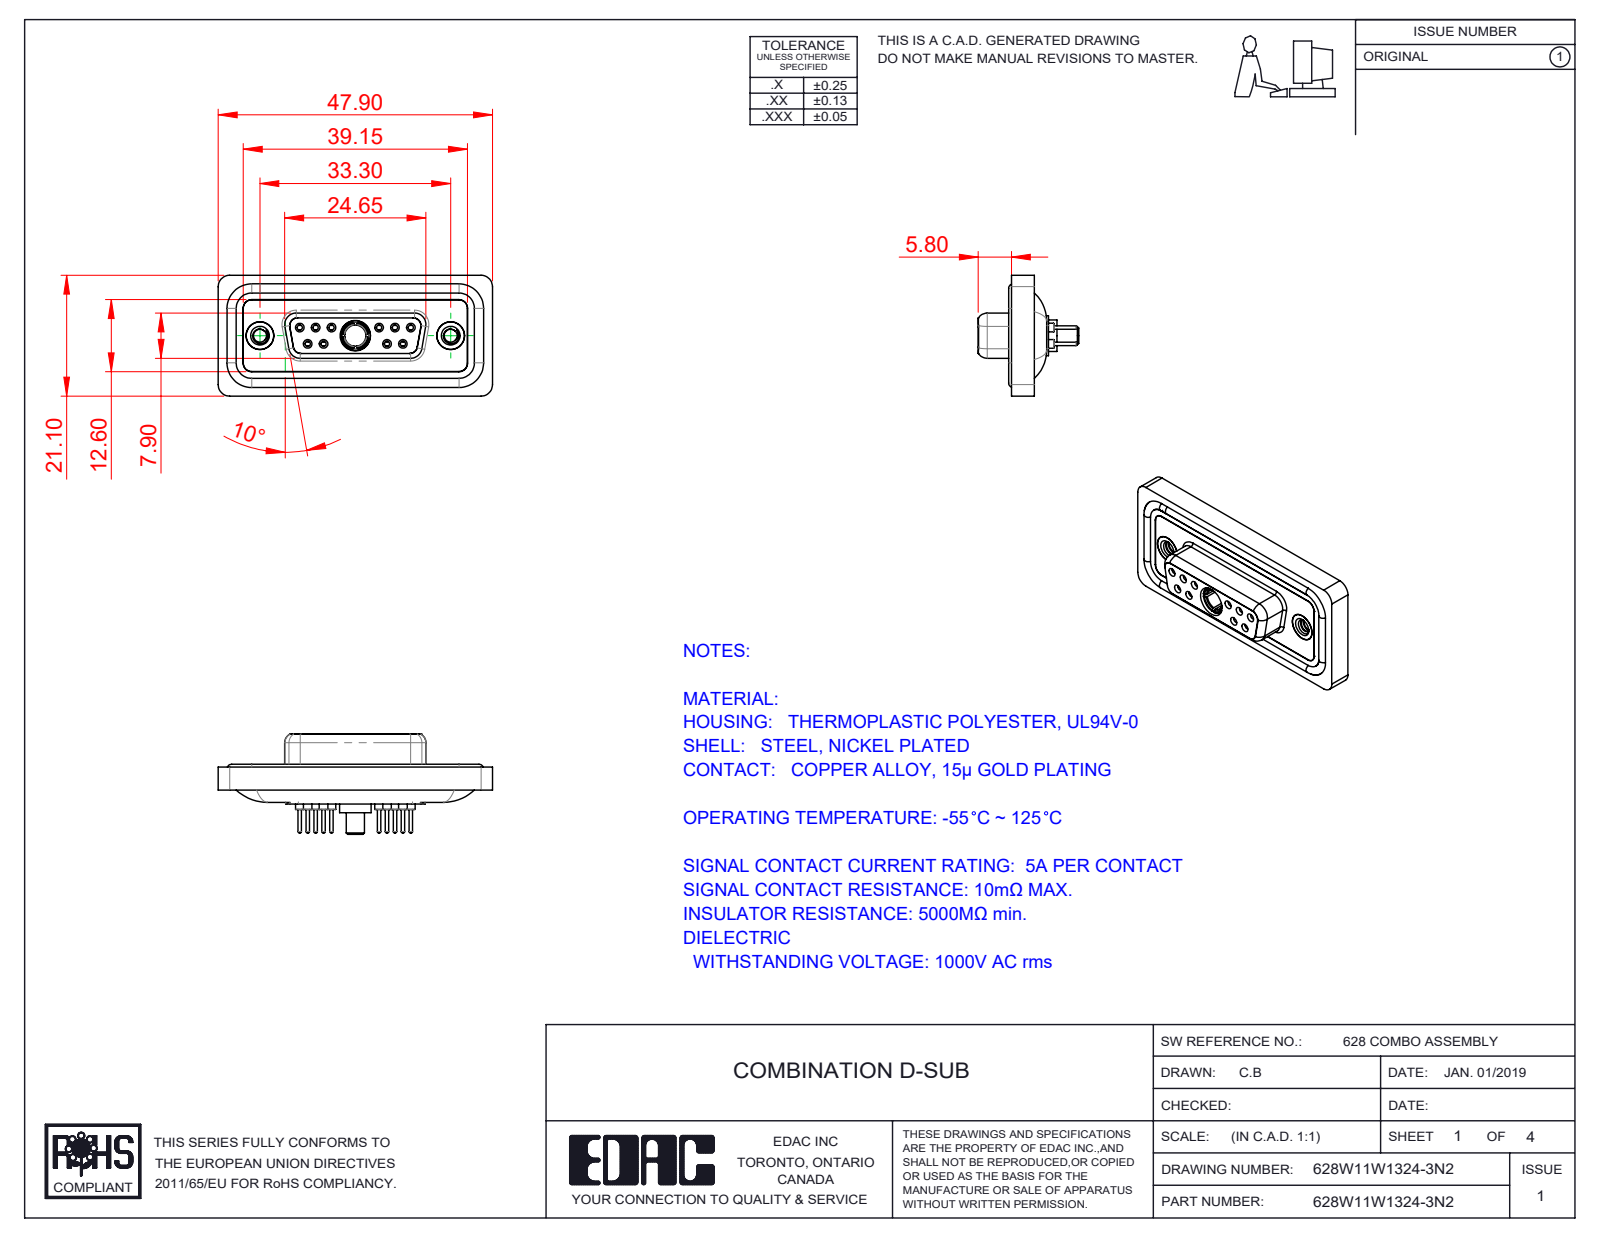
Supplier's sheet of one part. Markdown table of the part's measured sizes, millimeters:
| quantity | value |
| --- | --- |
| part name | 628Combo Contact Row 1_24; 628Combo Threaded Rivet_2; 628Combo Shell Front_15 Contacts; Power Socket_30A S (+5 more) |
| STEP written by | SolidWorks 2023 (CONFIG_CONTROL_DESIGN) |
| units | millimeters |
| bodies | 19 solids, 1010 faces (284 planar, 401 cylindrical, 325 other) |
| overall size | 47.9 × 21.1 × 17.55 |
| volume | 6 134 mm³ |
| surface area | 10 037 mm² |
| round holes (diameter × count) | 0.9 × 10, 1.1 × 10, 1.5 × 10, 2 × 10, 1.7 × 6, 1.6 × 4, 4.85 × 3, 2.26 × 2, 4 × 2, 4.05 × 2, 5 × 2, 3.7 × 1 |
| round bosses / shafts (diameter × count) | 2.2 × 10, 1.6 × 10, 0.6 × 10, 4.95 × 2, 4.8 × 2, 5.5 × 1, 5.2 × 1, 4.96 × 1 |
| partial cylindrical surfaces (radius × count) | 1.5 × 22, 2 × 20, 1.35 × 12, 1.6 × 8, 0.25 × 4, 0.5 × 4, 0.6 × 4, 0.65 × 4 |
| main face-to-face distances | 0.4, 1.6, 1.8, 2.9, 0.5, 1.1, 5.65, 7.45, 6.6, 7.05 |
| hole center spacings | 3.16, 2.77, 13.85, 11.08, 16.62, 5.03, 5.04, 5.54 |
